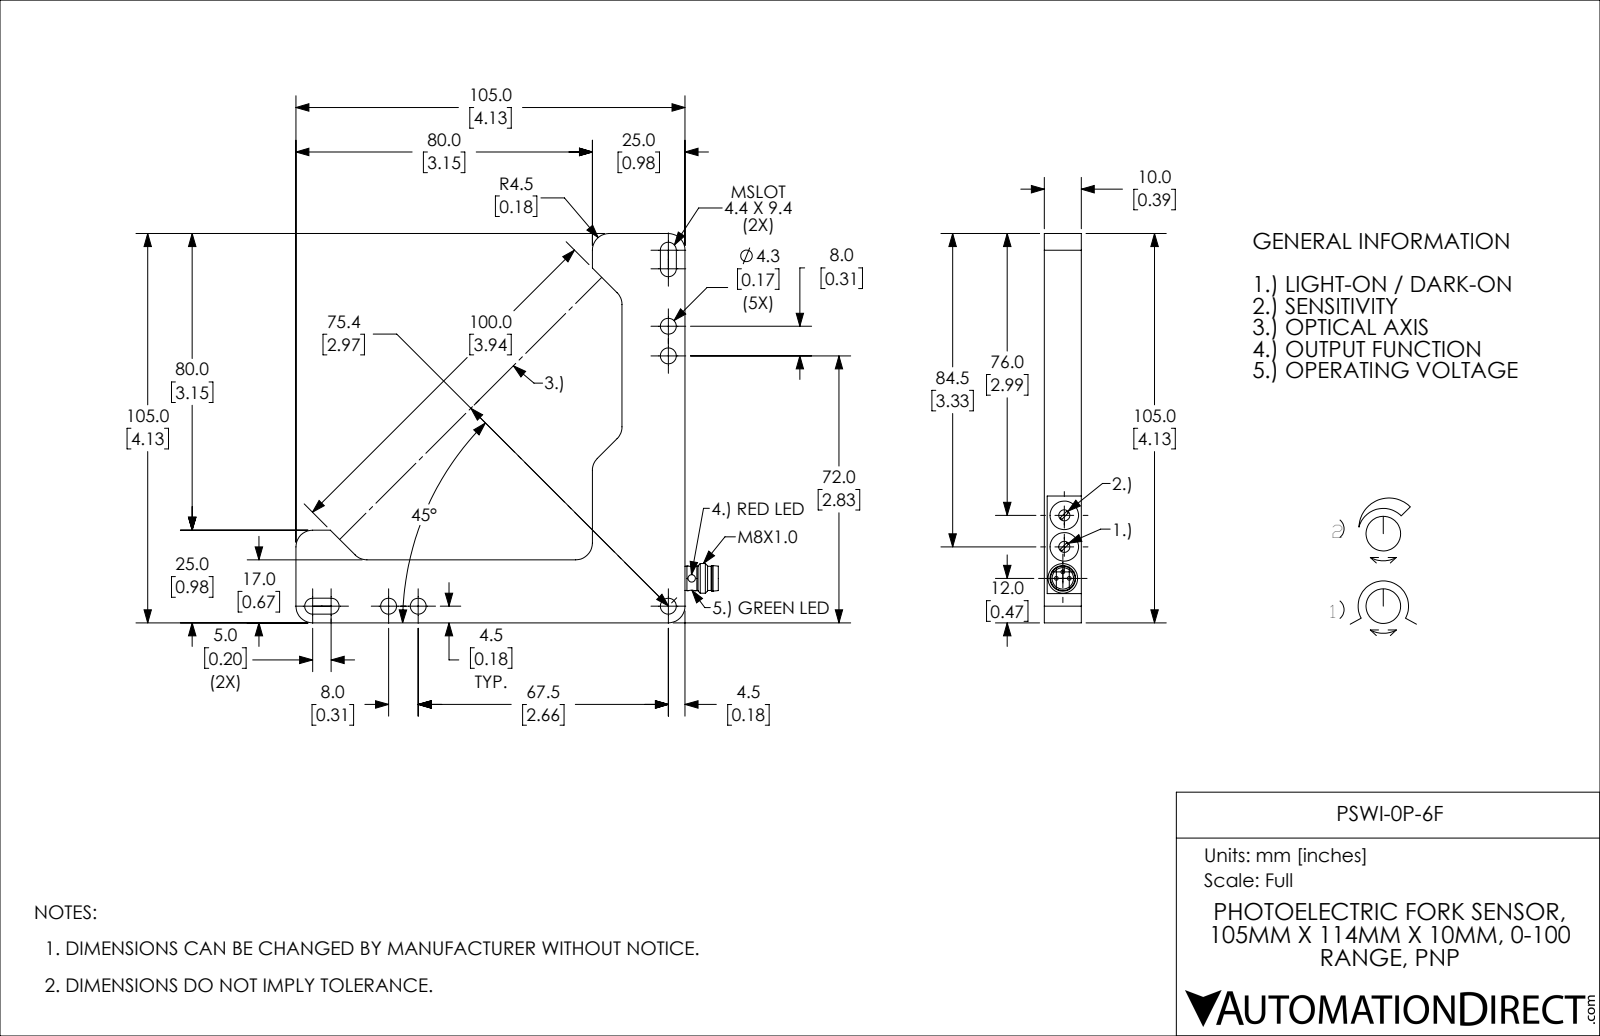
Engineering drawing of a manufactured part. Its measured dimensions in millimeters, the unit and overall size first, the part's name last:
Units: millimetres
Overall size (bounding box): 114 × 105 × 10
Round holes (diameter × count): ⌀4.3 ×5, ⌀2 ×2, ⌀3 ×2, ⌀7.7 ×2, ⌀5.8 ×1
Round bosses / shafts (diameter × count): ⌀1 ×3, ⌀8 ×1, ⌀6.9 ×1, ⌀6.7 ×1, ⌀6.5 ×1
Partial cylindrical surfaces — rounded edges, fillets, slot ends (radius × count): R4.5 ×10, R2.2 ×4, R1.2 ×2
Main face-to-face distances: 10, 17, 105, 88, 25, 8, 80, 104.9, 24.9, 16.9
Hole centre spacings: 8, 67.5, 75.5, 101.3, 8.5, 8.5, 9.8, 17
Volume: 35 900 mm³ · Surface area: 12 920 mm²
Bodies: 1 solid, 90 faces (42 planar, 41 cylindrical, 7 other)
Part name (STEP PRODUCT): PSWI-0P-6F
STEP written by: SolidWorks 2017 (AUTOMOTIVE_DESIGN)
